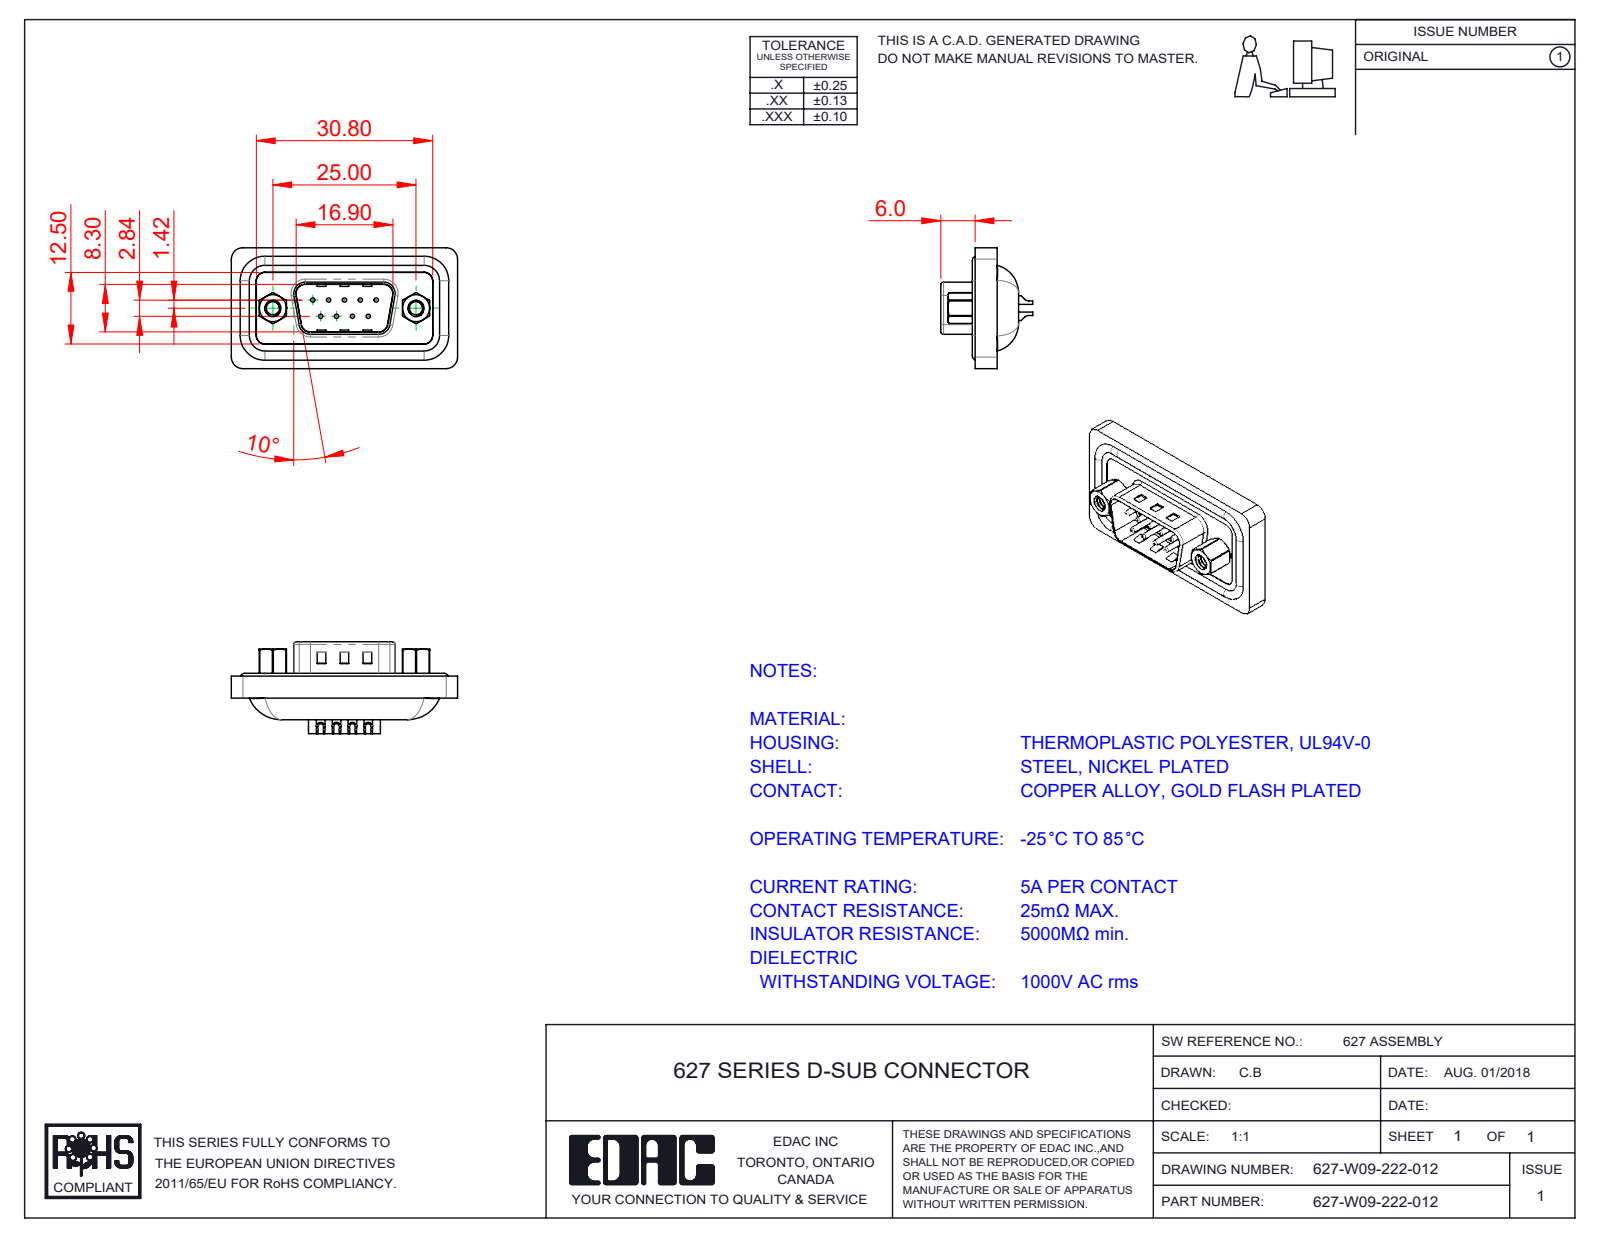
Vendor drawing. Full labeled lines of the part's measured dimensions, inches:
Part name (STEP PRODUCT): 627W 4-40 Threaded Rivet; 627W Housing_09 Contacts; 627W Contact Row 1_22; 627-W09-222-012 (+4 more)
STEP written by: SolidWorks 2023 (CONFIG_CONTROL_DESIGN)
Units: inches
Bodies: 17 solids, 799 faces (222 planar, 374 cylindrical, 203 other)
Overall size (bounding box): 1.555 × 0.831 × 0.64
Volume: 0.285 in³ · Surface area: 10.29 in²
Round holes (diameter × count): ⌀0.03 ×9, ⌀0.039 ×9, ⌀0.059 ×9, ⌀0.063 ×9, ⌀0.079 ×9, ⌀0.089 ×2, ⌀0.09 ×2, ⌀0.157 ×2, ⌀0.189 ×2, ⌀0.197 ×2
Round bosses / shafts (diameter × count): ⌀0.063 ×4, ⌀0.059 ×4, ⌀0.193 ×2, ⌀0.11 ×2
Partial cylindrical surfaces — rounded edges, fillets, slot ends (radius × count): R0.079 ×16, R0.059 ×14, R0.02 ×8, R0.106 ×6, R0.035 ×4, R0.063 ×4, R0.169 ×4, R0.016 ×2
Main face-to-face distances: 0.016, 0.03, 0.043, 0.108, 0.02, 0.148, 0.039, 0.138, 0.073, 0.063
Hole centre spacings: 0.124, 0.109, 0.218, 0.198, 0.198, 0.294, 0.295, 0.327
